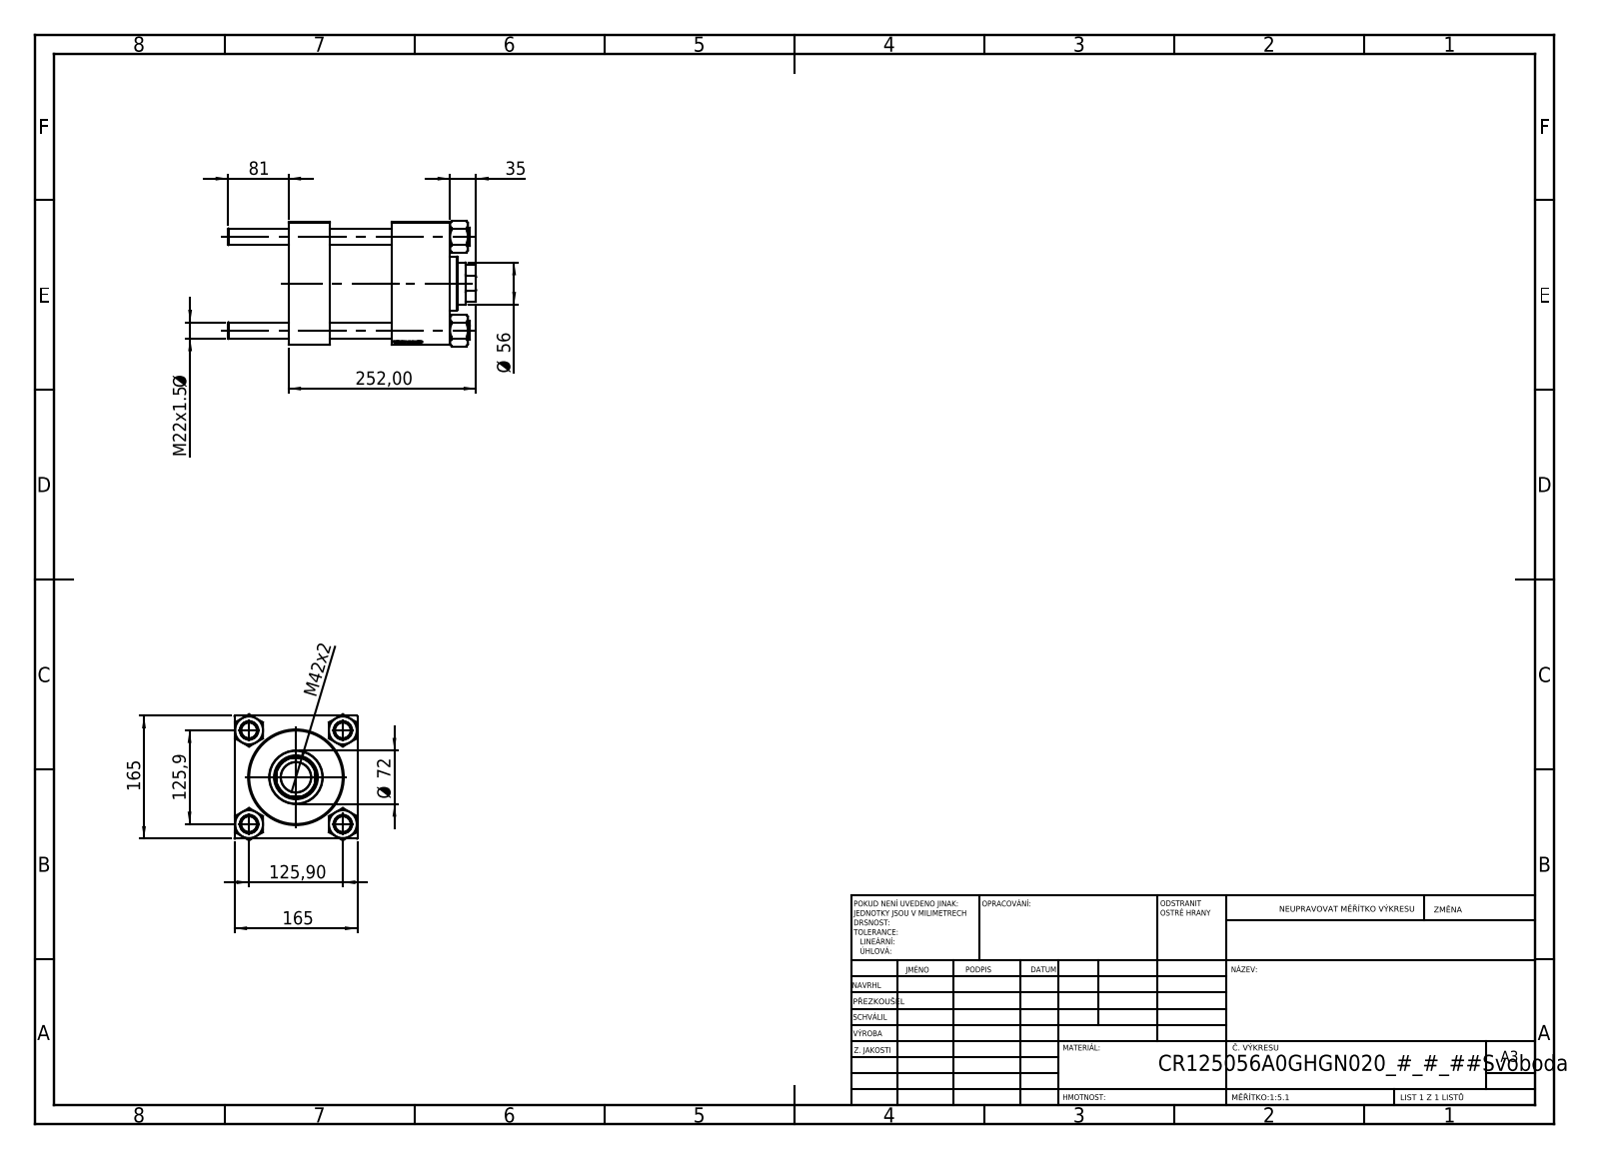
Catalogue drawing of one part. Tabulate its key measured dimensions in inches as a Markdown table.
| quantity | value |
| --- | --- |
| part name | V215CR_BODY_A; NUT_M5; V215_VC_A; V215CR_VCP (+1 more) |
| STEP written by | SolidWorks 2019 (CONFIG_CONTROL_DESIGN) |
| units | inches |
| bodies | 11 solids, 1182 faces (568 planar, 78 cylindrical, 536 other) |
| overall size | 13.11 × 6.659 × 6.496 |
| volume | 285.6 in³ |
| surface area | 850.4 in² |
| round holes (diameter × count) | 0.866 × 4, 0.276 × 2, 1.269 × 2, 1.772 × 2, 1.594 × 1, 2.205 × 1, 2.323 × 1, 3.78 × 1, 4.921 × 1, 4.941 × 1 |
| round bosses / shafts (diameter × count) | 0.984 × 4, 5.157 × 1, 2.835 × 1 |
| partial cylindrical surfaces (radius × count) | 1.063 × 1 |
| main face-to-face distances | 6.496, 2.165, 6.378, 8.543, 5.472, 3.307, 3.071, 7.413, 5.248, 1.941 |
| hole center spacings | 3.505, 4.957, 7.01, 5.453 |
